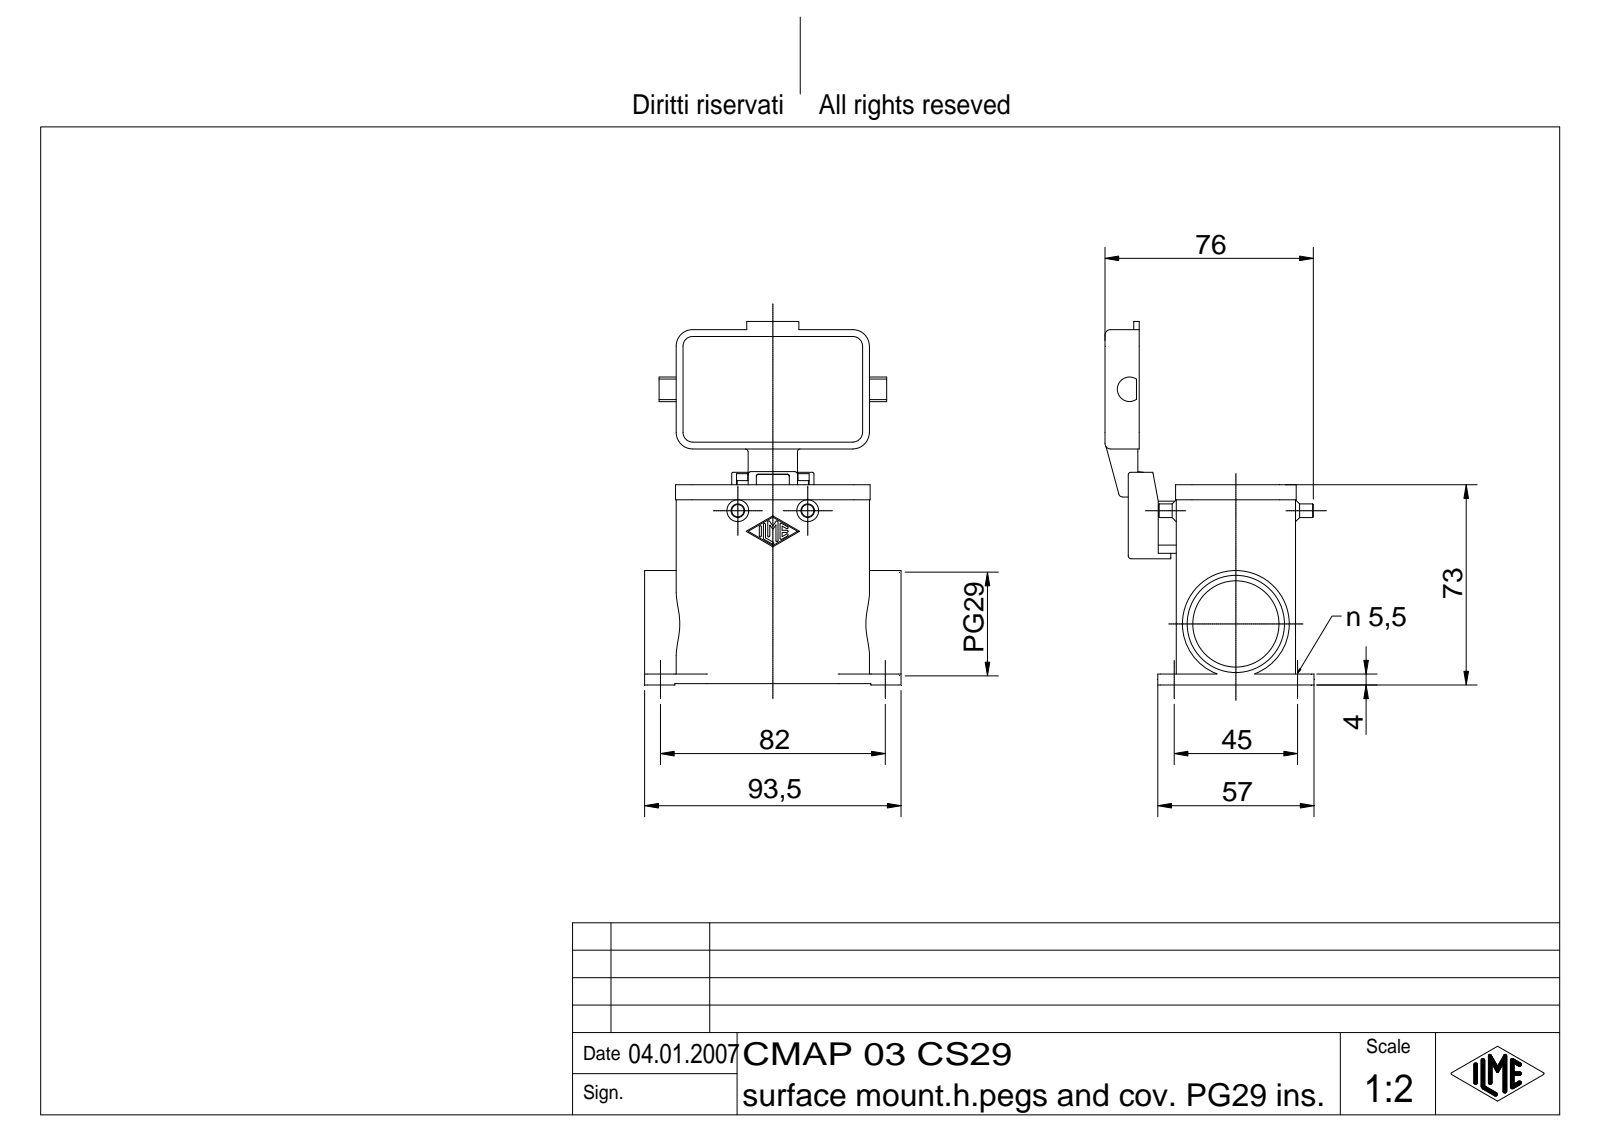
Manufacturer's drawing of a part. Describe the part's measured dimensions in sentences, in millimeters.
The part is named "CMAP 03 CS29". Its 3-D file was written by "Autodesk Inventor 7 (AUTOMOTIVE_DESIGN)". It is 2 solids with 479 faces: 179 planar, 179 cylindrical and 121 other. Overall it measures 132.5 by 93.5 by 76.25 millimeters. Its volume is 105 552 cubic millimeters and its surface area 60 857 square millimeters. Round holes: 4 of diameter 5.5, 1 of diameter 4, 1 of diameter 5, 1 of diameter 31.48, 1 of diameter 35.48. Round bosses or shafts: 2 of diameter 5, 2 of diameter 3, 1 of diameter 38.98, 1 of diameter 7, 1 of diameter 4. Partial cylindrical surfaces (rounded edges, fillets, slot ends): 26 of radius 1, 14 of radius 0.38, 12 of radius 6, 9 of radius 0.5, 8 of radius 0.7, 8 of radius 2, 4 of radius 3, 4 of radius 3.5. The main face-to-face distances are 3, 40.5, 3.5, 43.5, 37.5, 22.5, 66.5, 66, 63, 69.5. The hole center spacings are 45, 82, 93.54.
